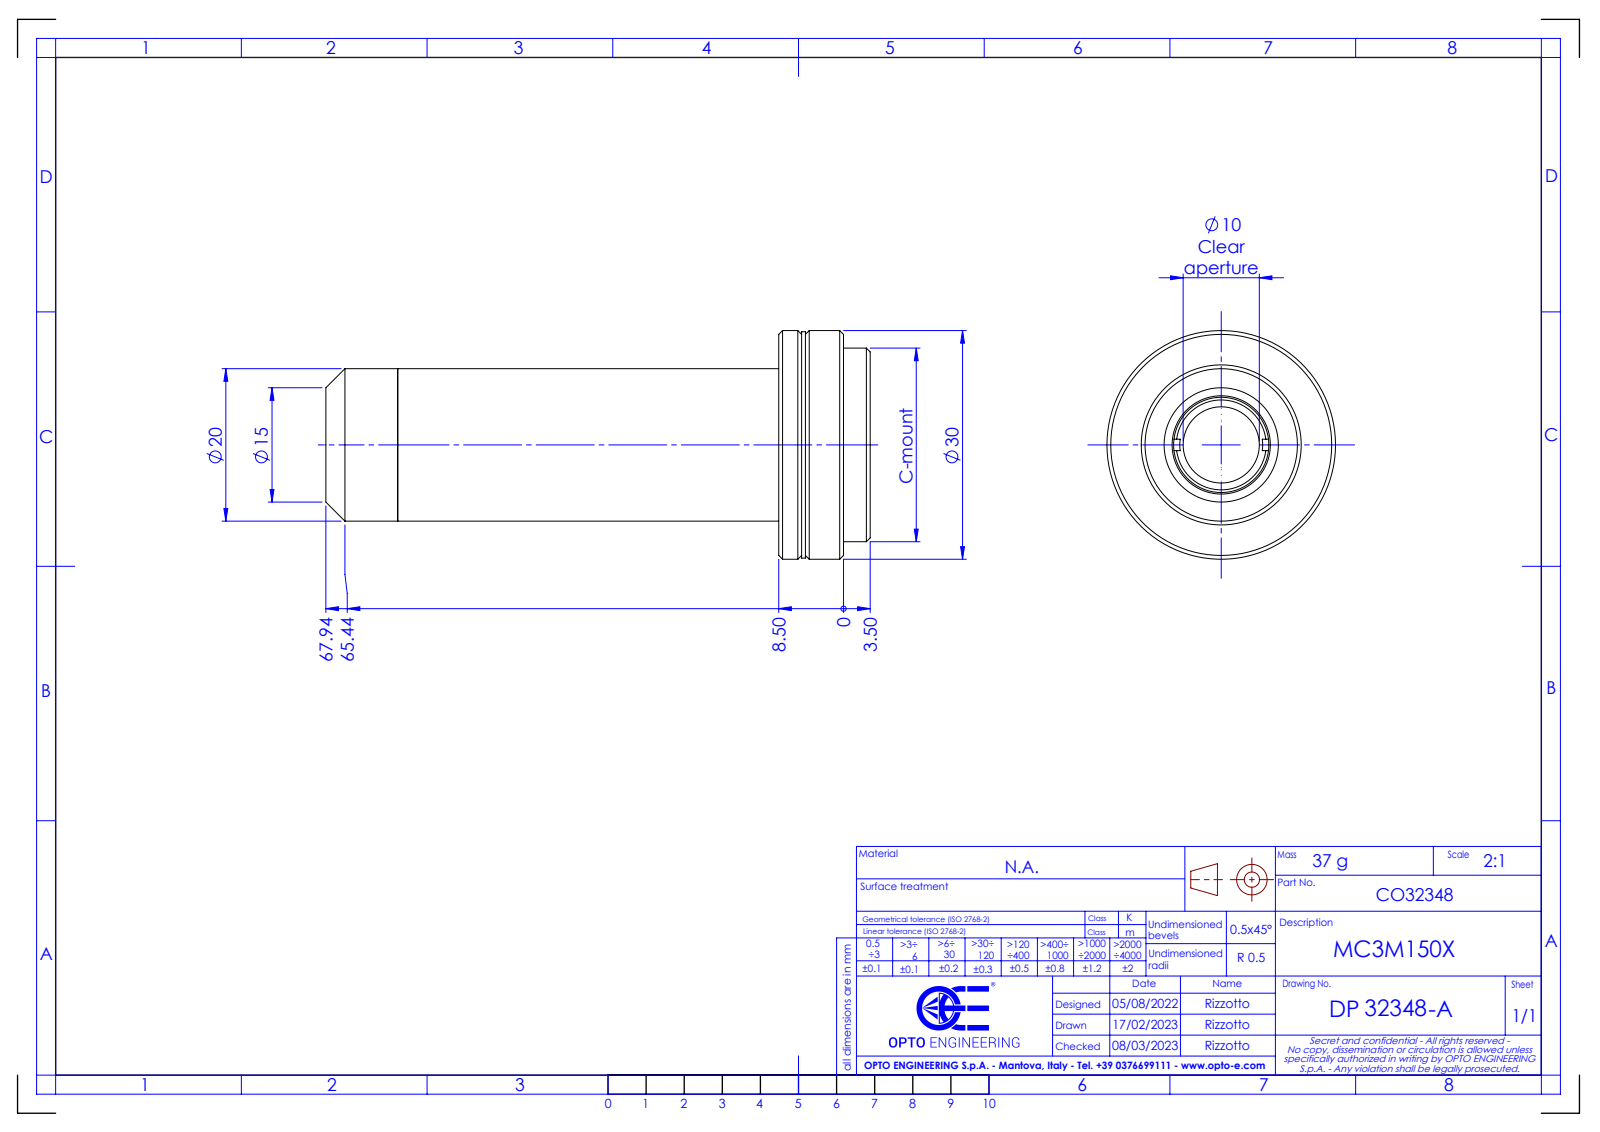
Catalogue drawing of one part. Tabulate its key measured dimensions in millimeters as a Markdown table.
| quantity | value |
| --- | --- |
| part name | DP32348-A_MC3M150X |
| STEP written by | SolidWorks 2021 (CONFIG_CONTROL_DESIGN) |
| units | millimeters |
| bodies | 0 solids, 65 faces (17 planar, 22 cylindrical, 26 other) |
| overall size | 71.44 × 30 × 30 |
| round holes (diameter × count) | 10 × 1, 12.5 × 1, 17.5 × 1, 18 × 1 |
| round bosses / shafts (diameter × count) | 30 × 1, 29.7 × 1, 25.4 × 1, 20 × 1 |
| main face-to-face distances | 8.5, 3.5, 5, 3, 0.5, 5.5, 12, 9, 50.01, 53.01 |
